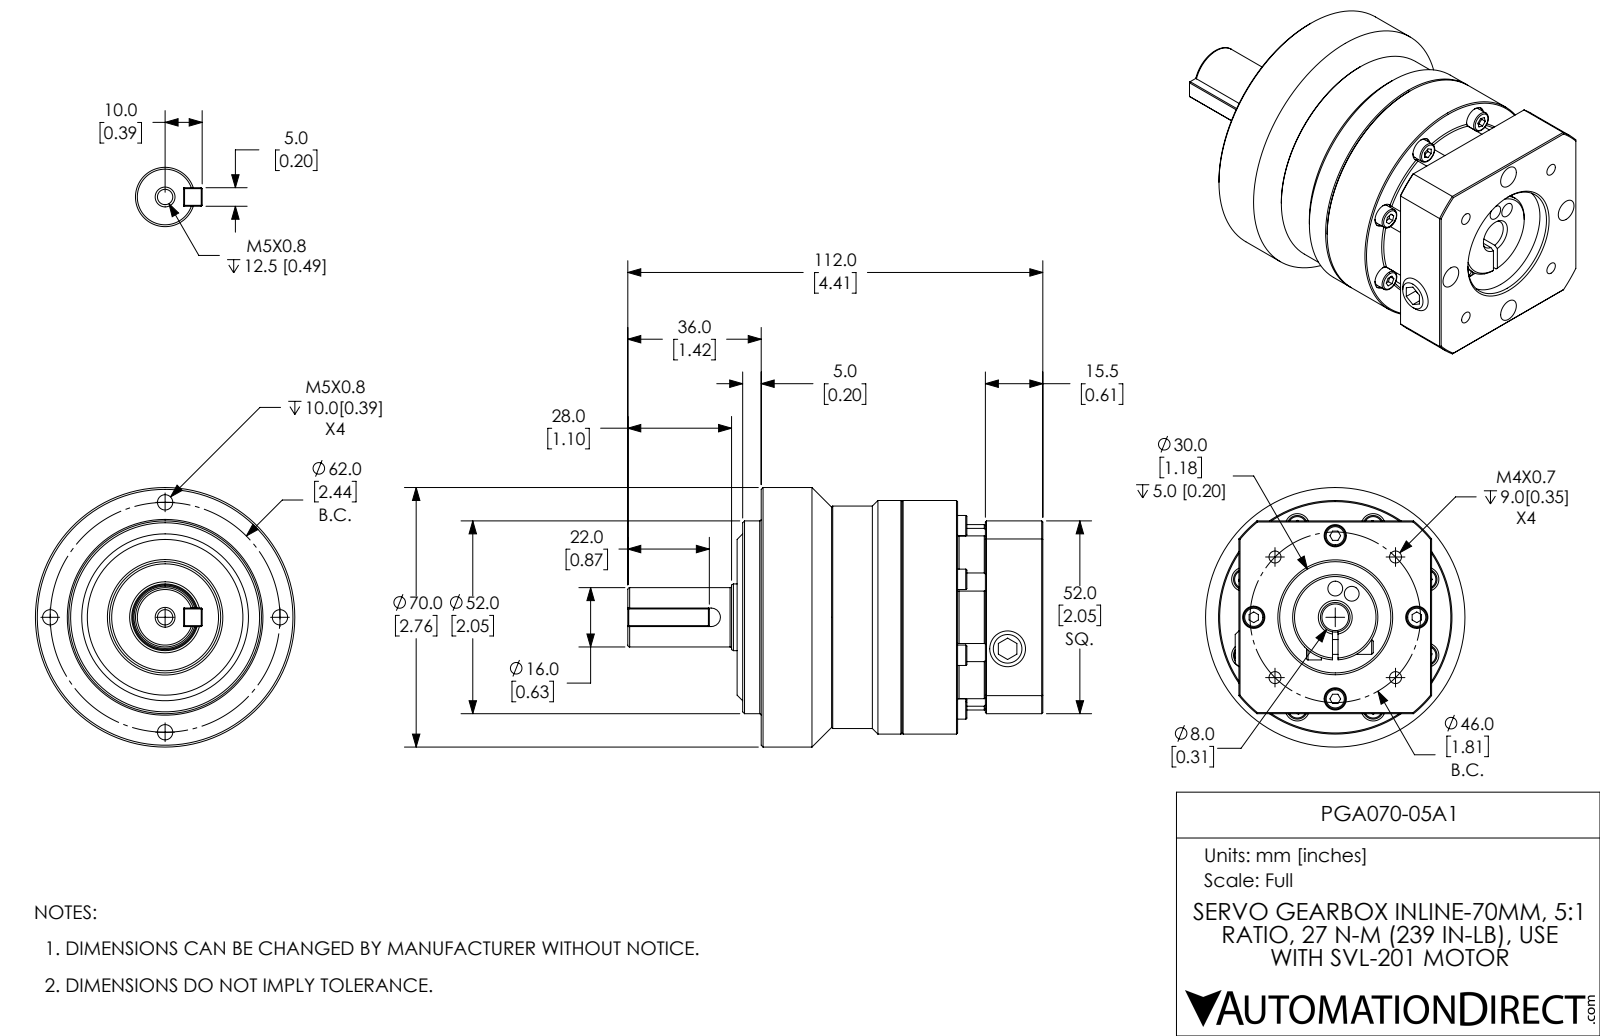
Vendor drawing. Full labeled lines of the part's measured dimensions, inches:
Part name (STEP PRODUCT): PGA070-05A1
STEP written by: SolidWorks 2019 (CONFIG_CONTROL_DESIGN)
Units: inches
Bodies: 1 solid, 447 faces (176 planar, 117 cylindrical, 154 other)
Overall size (bounding box): 4.409 × 2.756 × 2.756
Volume: 14.28 in³ · Surface area: 52.64 in²
Round holes (diameter × count): ⌀0.256 ×8, ⌀0.163 ×5, ⌀0.128 ×4, ⌀0.236 ×4, ⌀0.157 ×2, ⌀0.315 ×2, ⌀0.177 ×1, ⌀1.181 ×1, ⌀1.339 ×1
Round bosses / shafts (diameter × count): ⌀0.217 ×12, ⌀2.756 ×1, ⌀2.48 ×1, ⌀2.362 ×1, ⌀2.047 ×1, ⌀0.906 ×1, ⌀0.709 ×1, ⌀0.63 ×1
Partial cylindrical surfaces — rounded edges, fillets, slot ends (radius × count): R0.098 ×1, R0.157 ×1, R0.984 ×1, R1.319 ×1
Main face-to-face distances: 2.992, 0.61, 2.382, 2.638, 2.047, 0.256, 0.197, 3.248, 0.295, 2.087
Hole centre spacings: 0.409, 0.417, 0.473, 0.679, 0.864, 1.053, 1.078, 1.095
